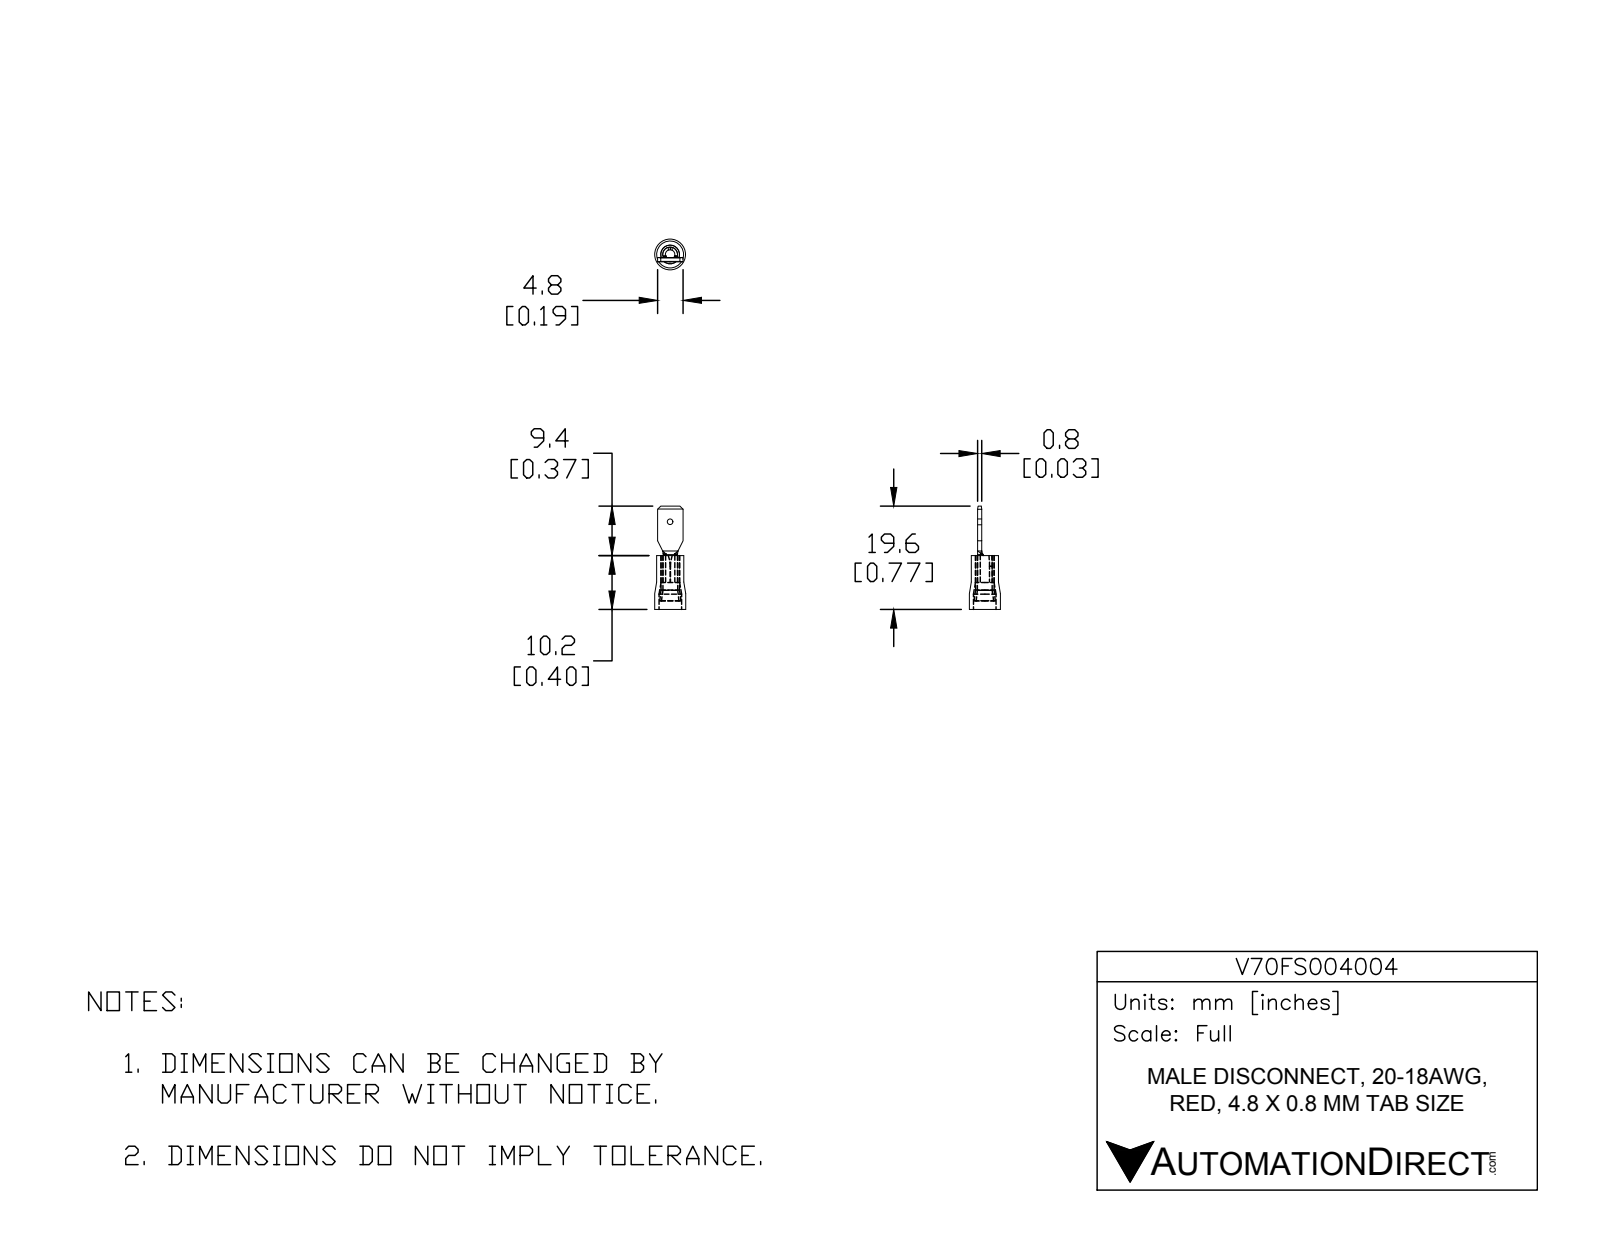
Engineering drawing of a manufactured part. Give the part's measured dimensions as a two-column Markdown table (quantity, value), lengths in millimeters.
| quantity | value |
| --- | --- |
| part name | V70FS004004 |
| STEP written by | SolidWorks 2017 (AUTOMOTIVE_DESIGN) |
| units | millimeters |
| bodies | 3 solids, 59 faces (19 planar, 22 cylindrical, 18 other) |
| overall size | 19.59 × 5.87 × 5.87 |
| volume | 198 mm³ |
| surface area | 681 mm² |
| round holes (diameter × count) | 1.1 × 1, 1.76 × 1, 2.8 × 1, 3.53 × 1, 4.27 × 1 |
| round bosses / shafts (diameter × count) | 5.87 × 1, 5.13 × 1, 3.5 × 1, 2.76 × 1 |
| partial cylindrical surfaces (radius × count) | 5.89 × 2 |
| main face-to-face distances | 0.8, 10.19, 4.8, 5.19, 5, 2.37, 2.43, 19.59, 14.4, 9.4 |
